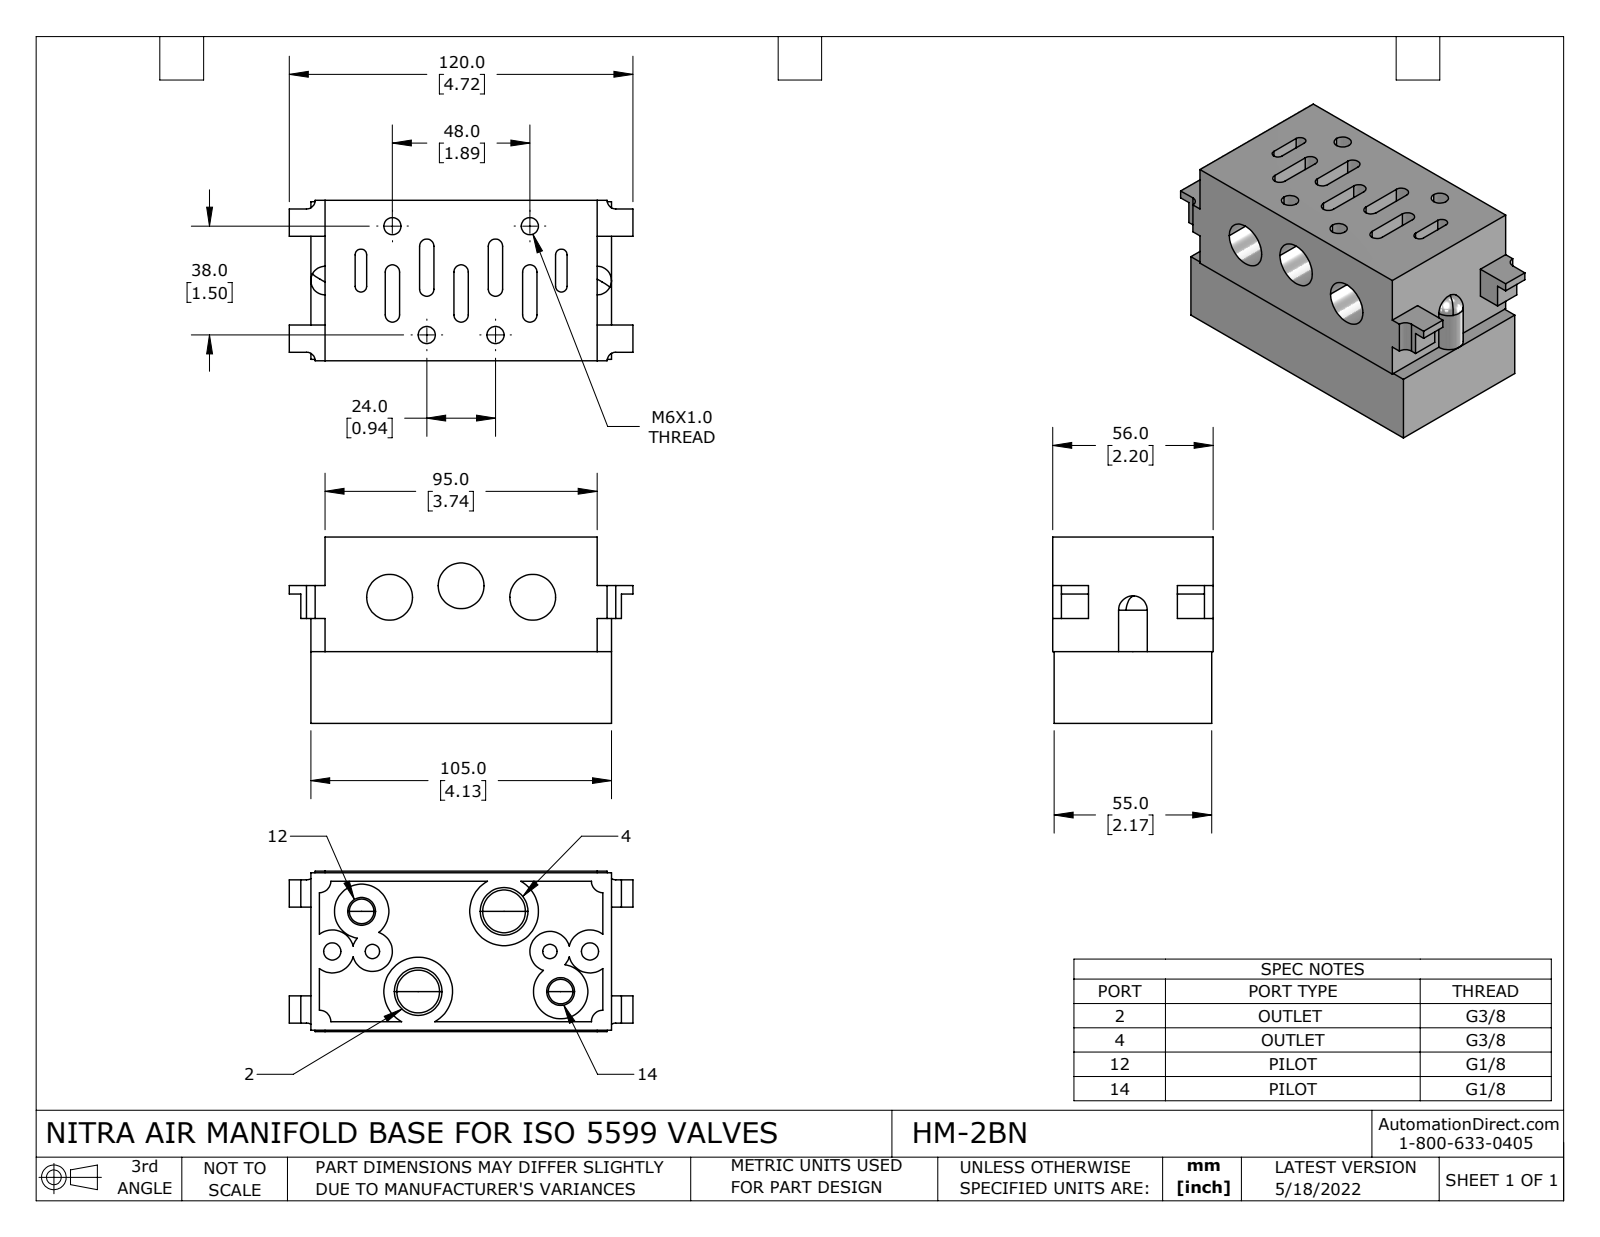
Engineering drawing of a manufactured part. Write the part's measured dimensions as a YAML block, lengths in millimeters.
part_name: "HM-2BN"
step_written_by: "SolidWorks 2021 (CONFIG_CONTROL_DESIGN)"
units: millimeters
bodies: {solids: 1, faces: 177, planar: 85, cylindrical: 72, other: 20}
overall_size: [120, 65, 56]
volume: 255341
surface_area: 60152
round_holes:
  - {diameter: 6, count: 6}
  - {diameter: 16, count: 3}
  - {diameter: 21, count: 3}
  - {diameter: 5, count: 2}
  - {diameter: 8.57, count: 2}
  - {diameter: 14.95, count: 2}
round_bosses_or_shafts:
  - {diameter: 24, count: 2}
  - {diameter: 19, count: 2}
partial_cylinders:
  - {radius: 2.5, count: 10}
  - {radius: 2, count: 4}
  - {radius: 3, count: 4}
  - {radius: 4, count: 4}
  - {radius: 5, count: 2}
  - {radius: 7, count: 2}
  - {radius: 7.5, count: 2}
face_to_face_distances: [0.5, 55.5, 3, 5, 52.5, 3.5, 52, 45, 56, 55]
hole_center_spacings: [14, 14.49, 17.35, 20.25, 21.26, 25.32, 26.87, 28.32]
